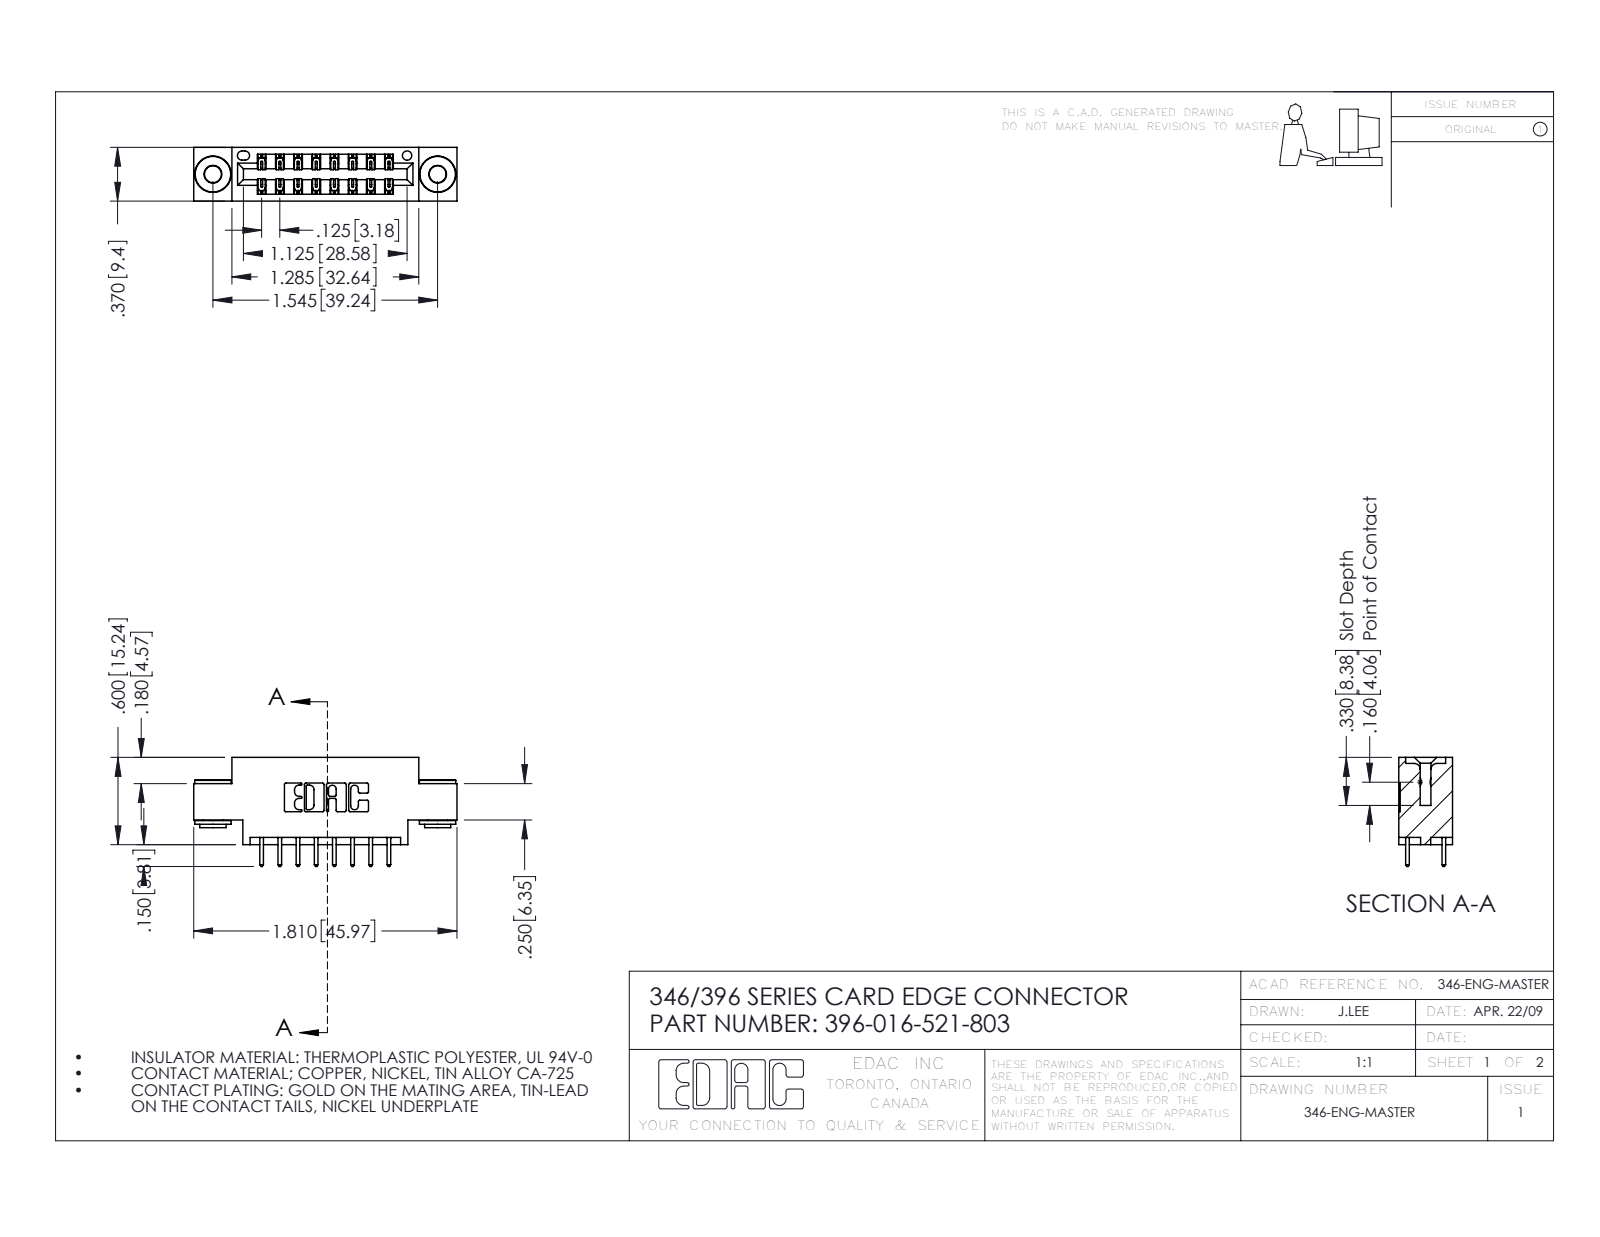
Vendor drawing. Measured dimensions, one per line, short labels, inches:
name: 396-016-521-803; 346 Part_0.170 Offset - 0.156 Dia-TH; 345-250-002_345-250-002-102; 345-292-001_345-293-121
written by: SolidWorks 2016 (CONFIG_CONTROL_DESIGN)
unit: in
bodies: 19 solids, 996 faces (650 planar, 338 cylindrical, 8 other)
size: 1.81 × 0.75 × 0.37
volume: 0.249 in³; area: 8.401 in²
holes: 2× ⌀0.116, 2× ⌀0.156, 1× ⌀0.064
bosses: 2× ⌀0.25, 2× ⌀0.18, 2× ⌀0.136
rounds: 24× R0.006, 22× R0.01, 16× R0.01, 6× R0.007, 6× R0.031, 3× R0.026, 2× R0.014, 2× R0.022
face distances: 0.25, 0.37, 0.048, 0.322, 0.025, 0.275, 0.072, 0.298, 0.148, 0.222
hole spacings: 0.246, 1.341, 1.545
